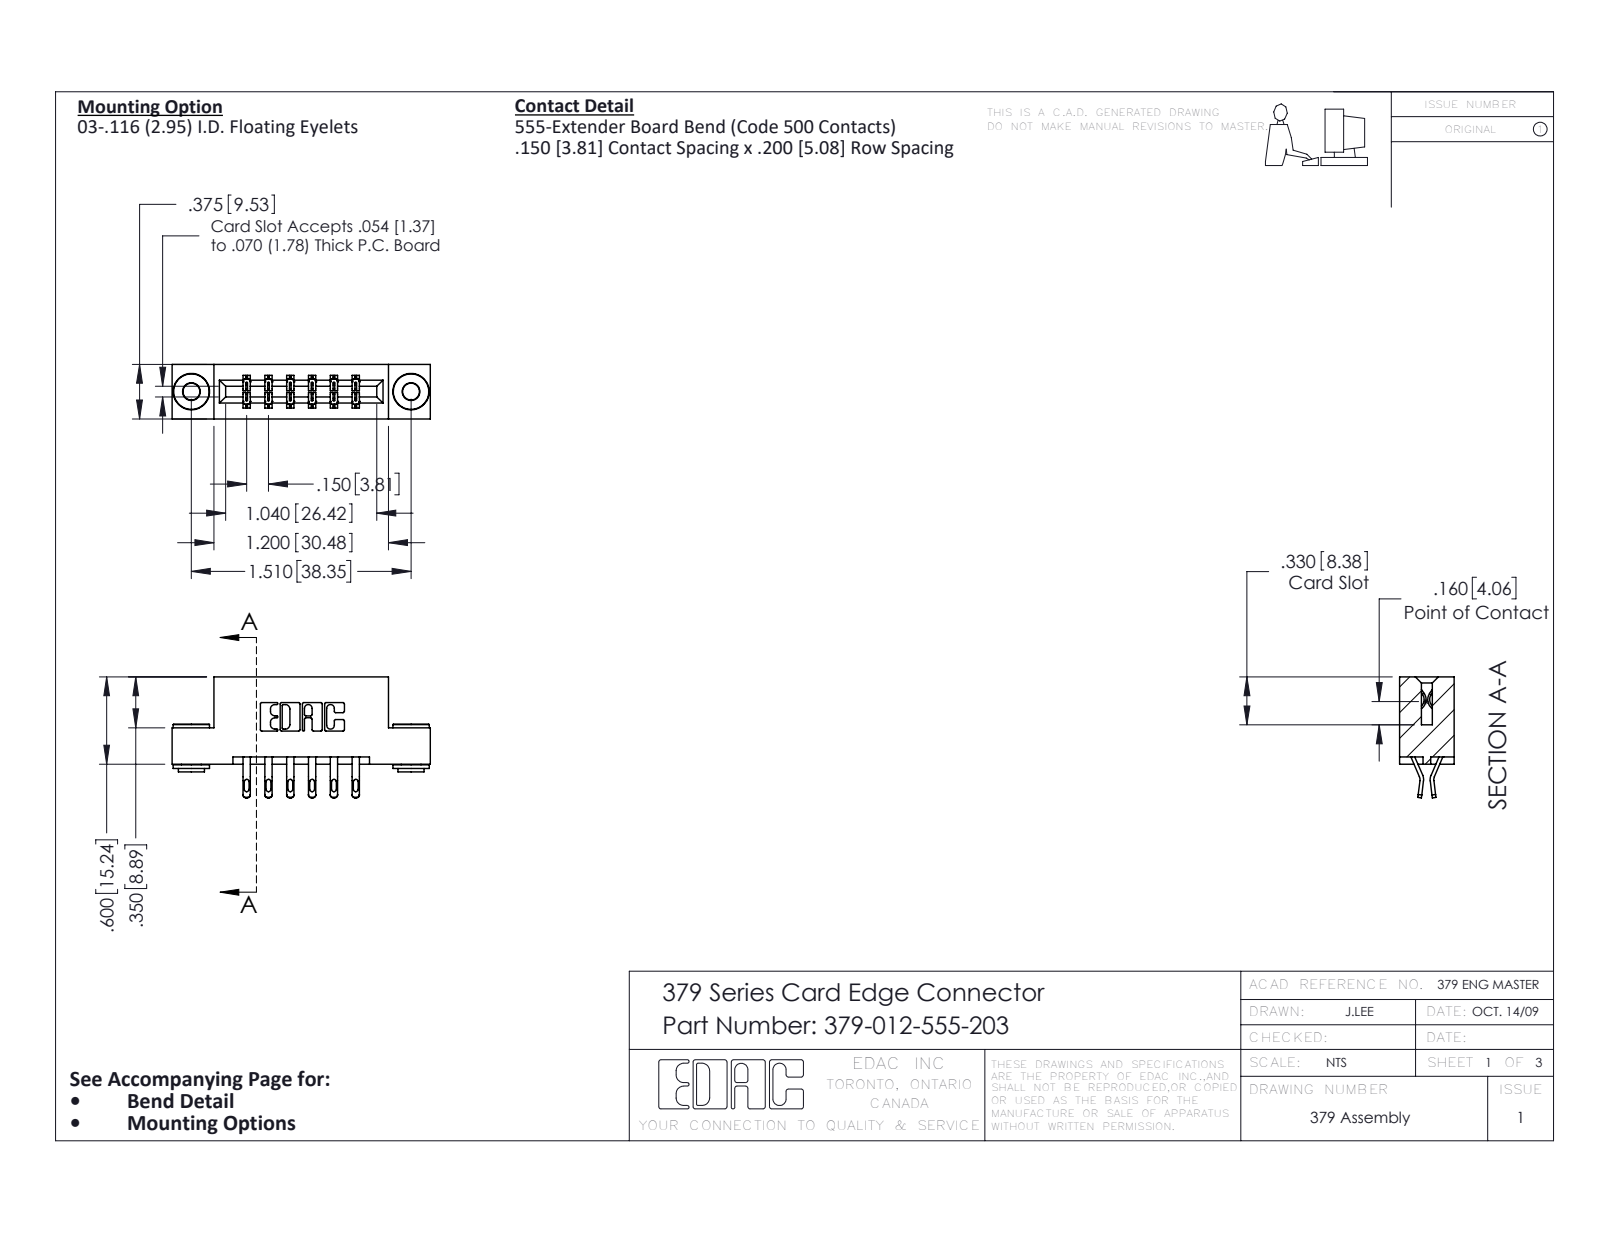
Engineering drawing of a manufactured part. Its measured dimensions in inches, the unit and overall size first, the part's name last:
Units: inches
Overall size (bounding box): 1.775 × 0.832 × 0.375
Round holes (diameter × count): ⌀0.116 ×2, ⌀0.156 ×2
Round bosses / shafts (diameter × count): ⌀0.25 ×2, ⌀0.18 ×2, ⌀0.136 ×2
Partial cylindrical surfaces — rounded edges, fillets, slot ends (radius × count): R0.016 ×24, R0.02 ×24, R0.01 ×22, R0.006 ×18, R0.007 ×6, R0.031 ×6, R0.026 ×3, R0.01 ×2
Main face-to-face distances: 0.3, 0.2, 0.15, 0.05, 0.25, 0.35, 0.375, 0.1, 0.55, 0.6
Hole centre spacings: 1.51
Volume: 0.269 in³ · Surface area: 7.701 in²
Bodies: 15 solids, 848 faces (488 planar, 352 cylindrical, 8 other)
Part name (STEP PRODUCT): 379 Part_Flush - .156 Dia - TH; 345-292-001_555 Tail; 345-250-002_345-250-002-102; 379-012-555-203
STEP written by: SolidWorks 2016 (CONFIG_CONTROL_DESIGN)
